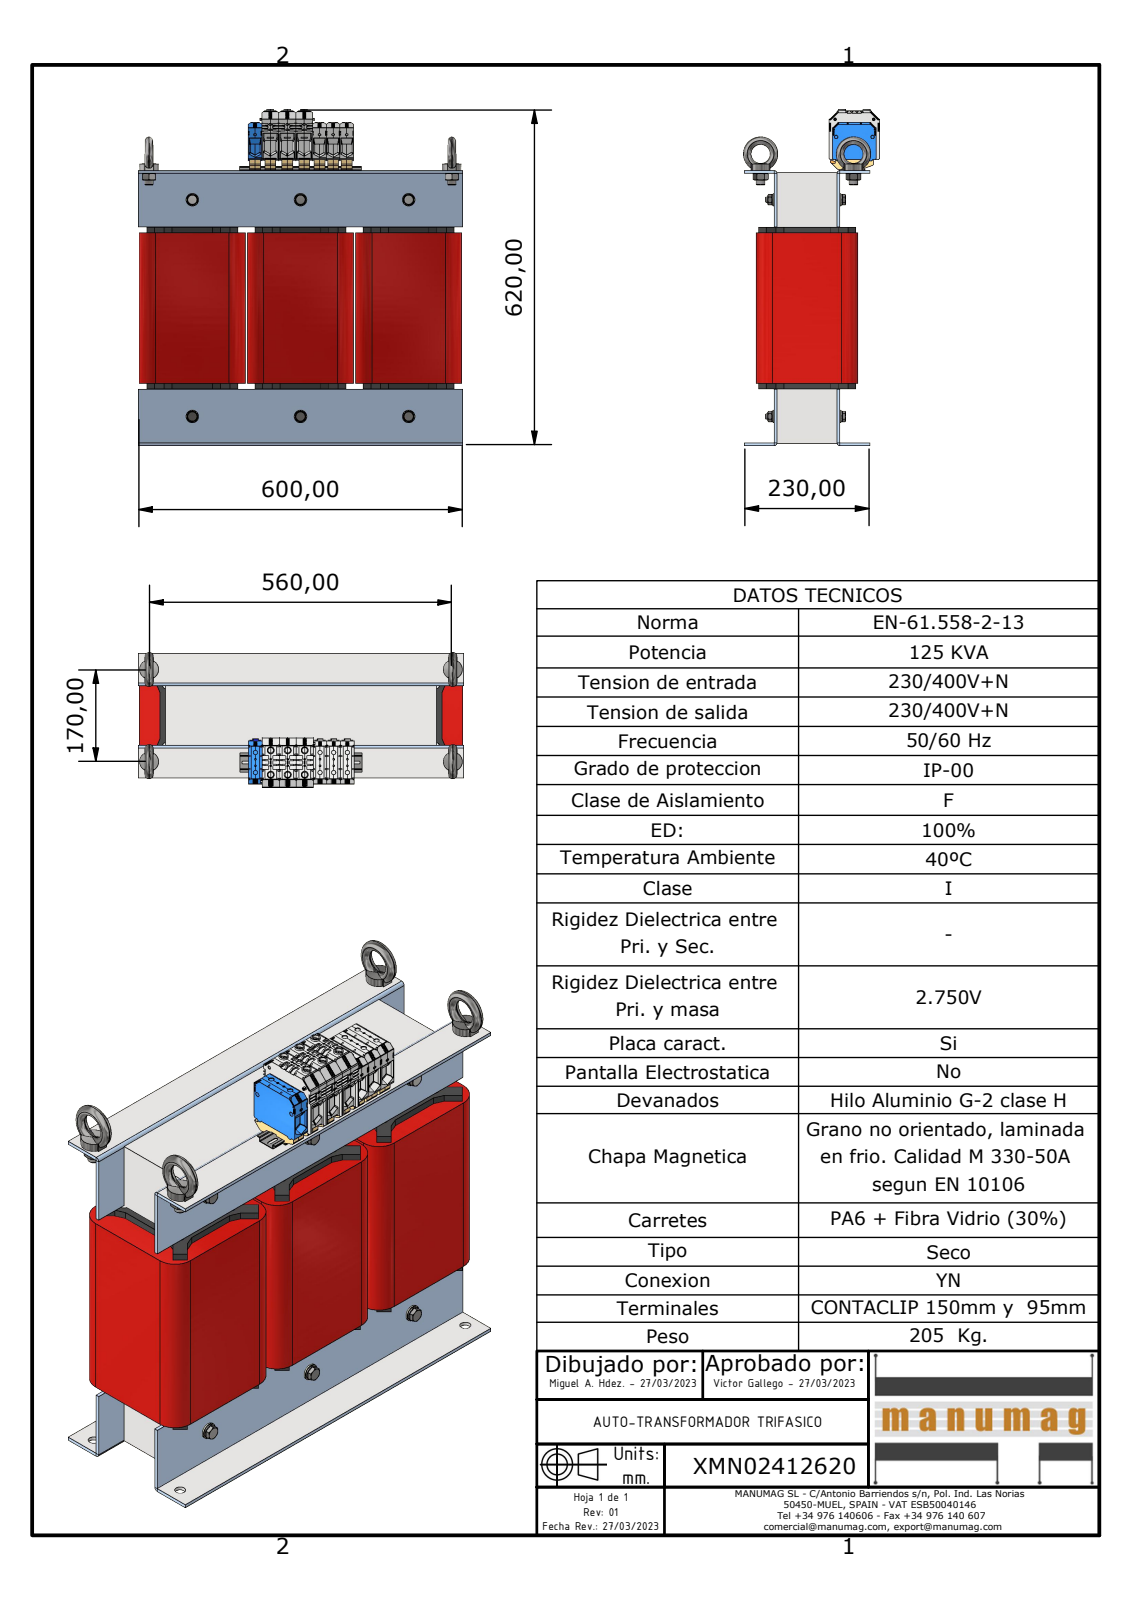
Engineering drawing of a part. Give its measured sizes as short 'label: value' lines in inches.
name: XMN02412620; 3UI300 500 x 500 - 110; CARRETE MECANO 100X110; BASE MECANO 100X110 (+8 more)
written by: Autodesk Inventor 2023 (AUTOMOTIVE_DESIGN)
unit: in
bodies: 91 solids, 7846 faces (4670 planar, 2332 cylindrical, 844 other)
size: 24.449 × 23.622 × 9.823
volume: 2 658 in³; area: 5 307 in²
holes: 24× ⌀0.394, 8× ⌀0.098, 8× ⌀0.108, 8× ⌀0.109, 8× ⌀0.116, 8× ⌀0.117, 8× ⌀0.315, 6× ⌀0.256, 6× ⌀0.33, 6× ⌀0.413, 6× ⌀0.669, 6× ⌀0.827
bosses: 6× ⌀0.906, 6× ⌀0.787, 6× ⌀0.606, 6× ⌀0.512, 6× ⌀0.453, 6× ⌀0.362, 4× ⌀0.63, 4× ⌀0.583
rounds: 321× R0.012, 212× R0.039, 72× R0.079, 18× R0.102, 12× R0.004, 12× R0.054, 12× R0.058, 12× R1.181
face distances: 4.331, 5.827, 1.496, 7.874, 0.197, 4.528, 3.937, 15.748, 0.394, 1.299
hole spacings: 7.874, 3.937, 5.853, 15.748, 1.232, 1.393, 1.667, 8.986
